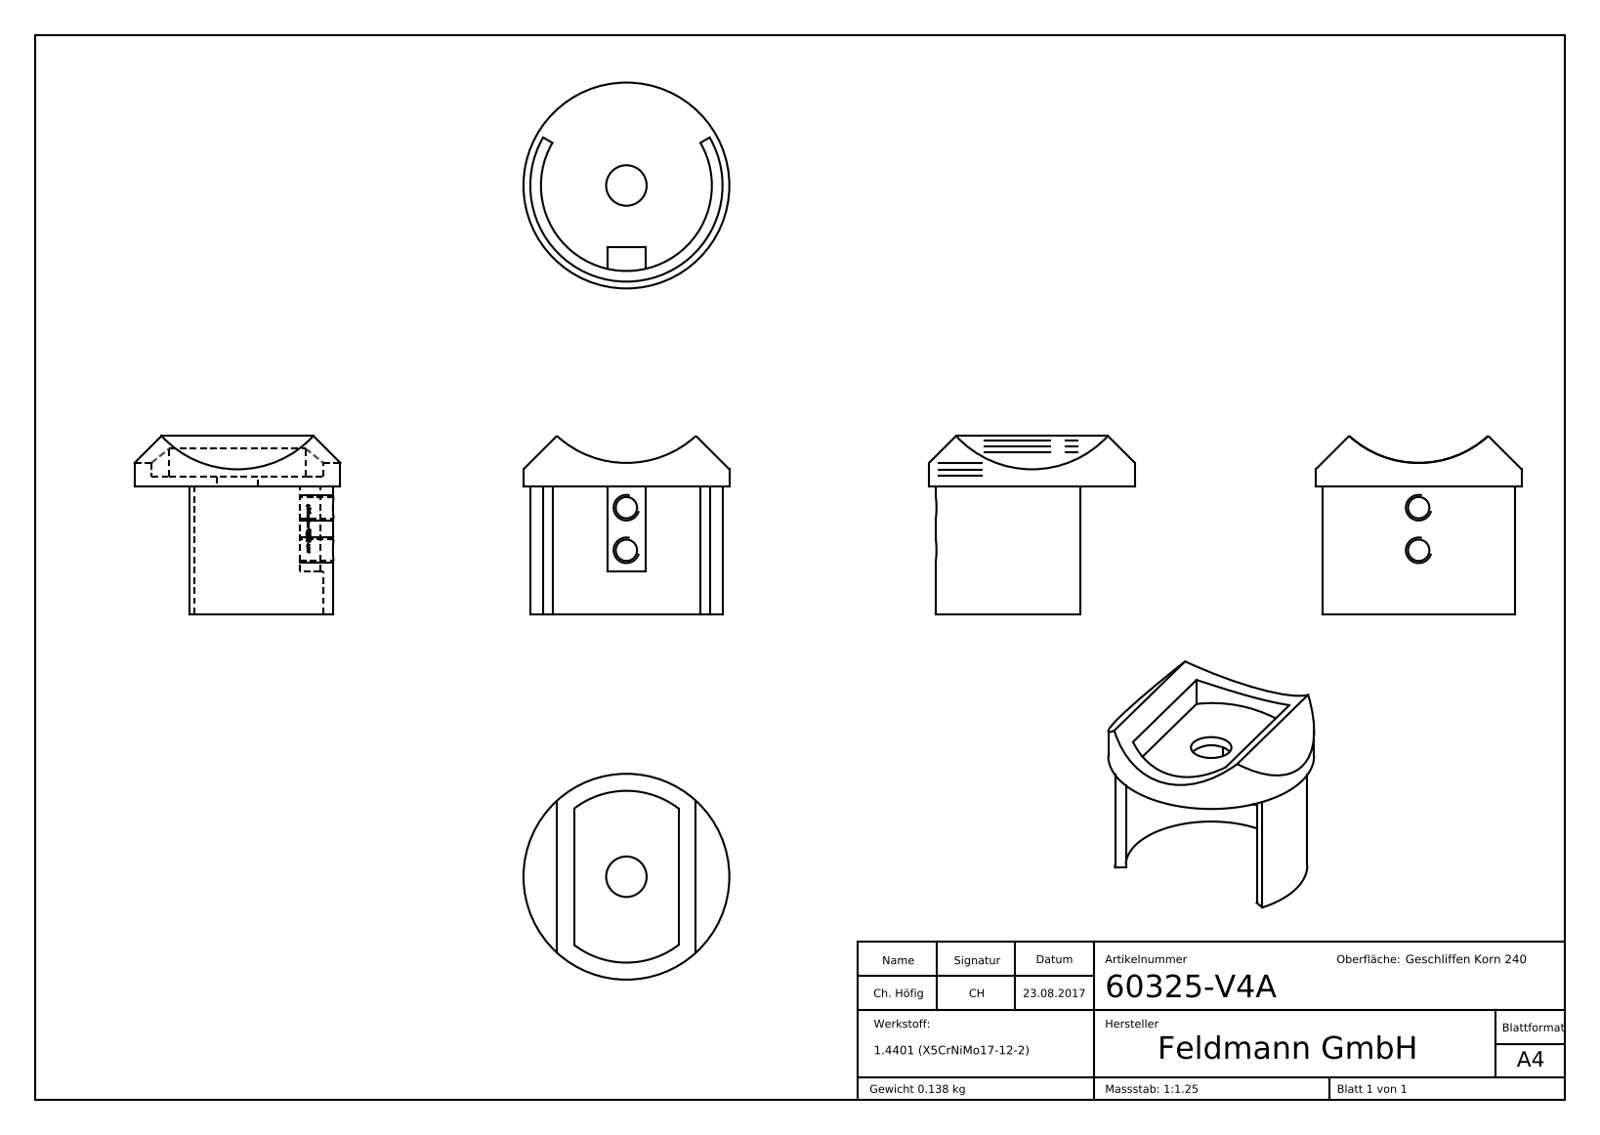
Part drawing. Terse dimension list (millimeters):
name: 60325-V4A
written by: SolidWorks 2015 (CONFIG_CONTROL_DESIGN)
unit: mm
bodies: 1 solid, 252 faces (144 planar, 14 cylindrical, 94 other)
size: 48.3 × 48.3 × 41.84
volume: 17 209 mm³; area: 11 449 mm²
holes: 2× ⌀5, 1× ⌀9.5
bosses: 1× ⌀48.3
rounds: 1× R20.05, 1× R20.15, 1× R22.55, 1× R24.15
face distances: 2.3, 30, 32.3, 24.62, 7.81, 16.81, 9, 10, 20, 22.3
hole spacings: 10
